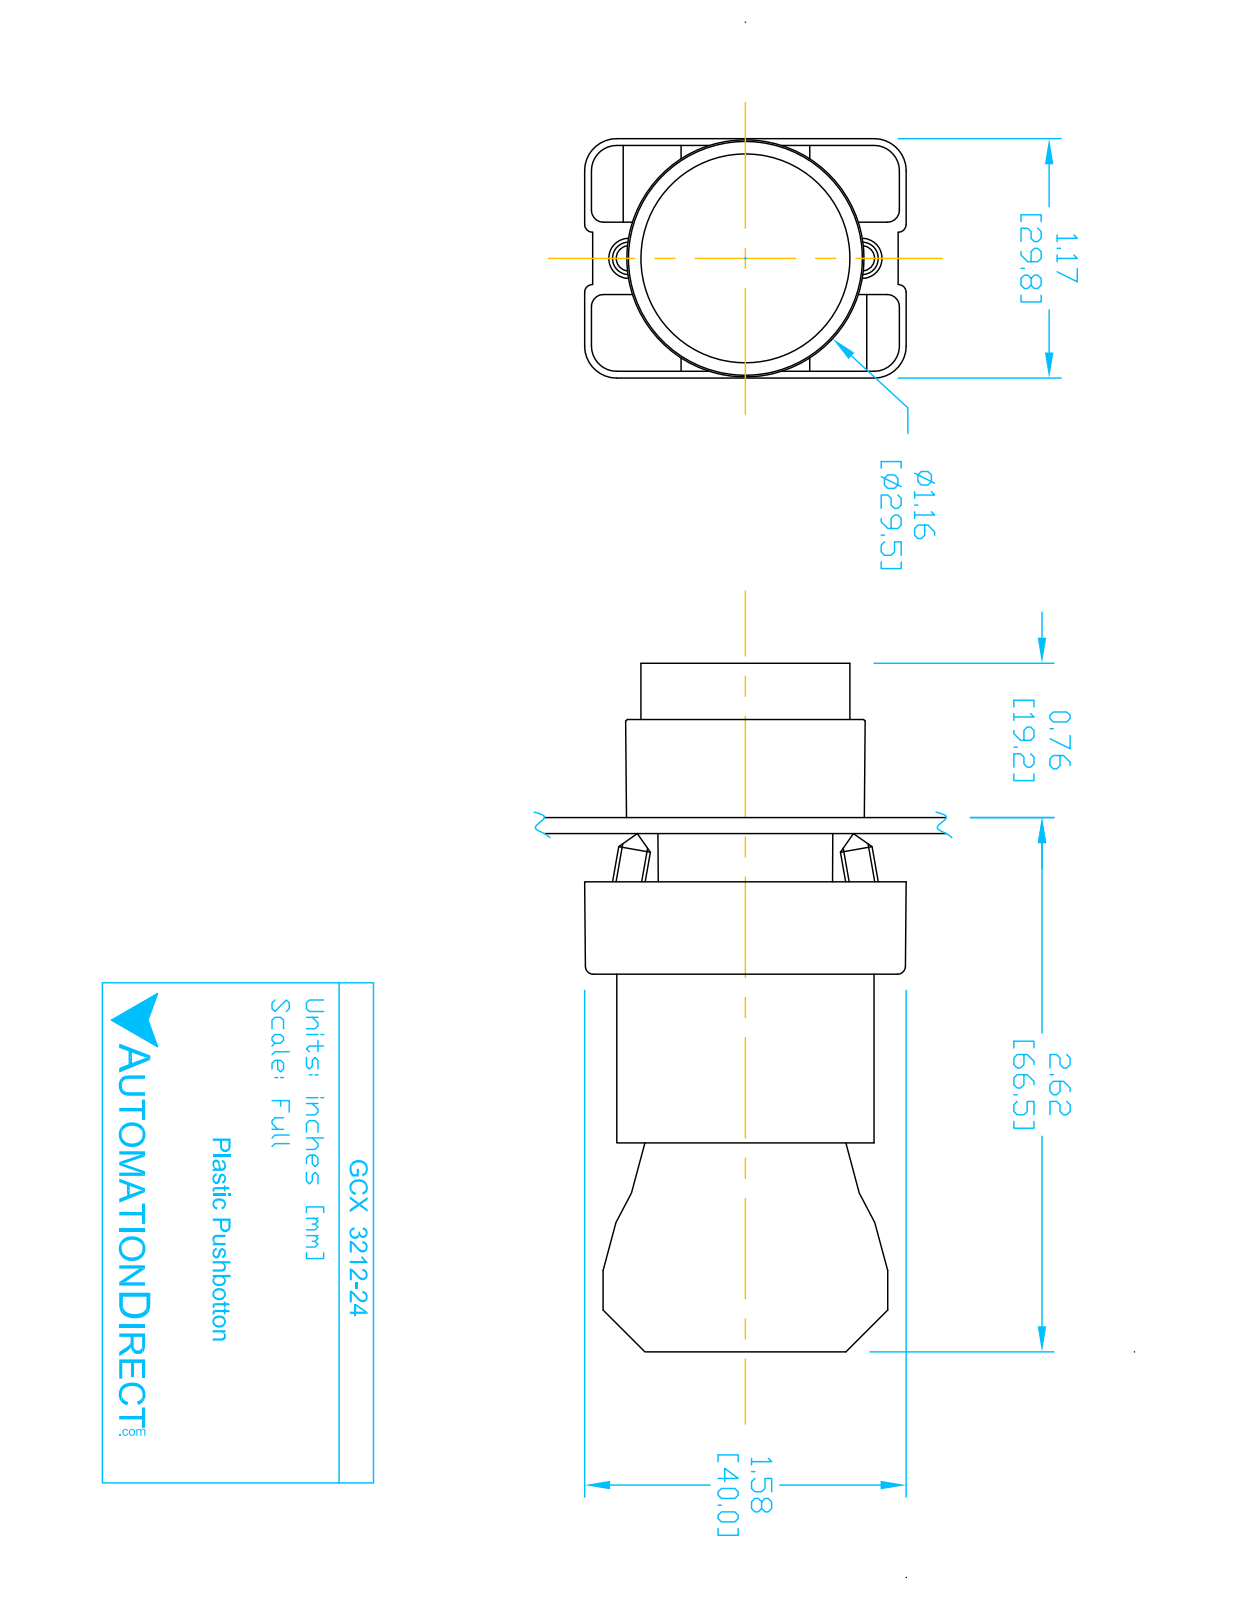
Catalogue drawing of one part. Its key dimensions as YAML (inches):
part_name: "ecx1040; GCX3212 OPERATOR; ECX3029-2; GCX3212-24 (+1 more)"
step_written_by: "SolidWorks 2016 (AUTOMOTIVE_DESIGN)"
units: inches
bodies: {solids: 7, faces: 425, planar: 250, cylindrical: 144, other: 31}
overall_size: [3.319, 1.581, 1.177]
volume: 2.721
surface_area: 36.32
round_holes:
  - {diameter: 0.079, count: 2}
  - {diameter: 0.124, count: 2}
  - {diameter: 0.13, count: 2}
  - {diameter: 0.087, count: 1}
  - {diameter: 0.197, count: 1}
  - {diameter: 0.469, count: 1}
  - {diameter: 0.878, count: 1}
  - {diameter: 0.888, count: 1}
  - {diameter: 1.024, count: 1}
round_bosses_or_shafts:
  - {diameter: 0.157, count: 4}
  - {diameter: 1.175, count: 1}
  - {diameter: 1.004, count: 1}
  - {diameter: 0.945, count: 1}
  - {diameter: 0.856, count: 1}
  - {diameter: 0.78, count: 1}
  - {diameter: 0.504, count: 1}
partial_cylinders:
  - {radius: 0.059, count: 24}
  - {radius: 0.041, count: 12}
  - {radius: 0.124, count: 12}
  - {radius: 0.157, count: 12}
  - {radius: 0.039, count: 8}
  - {radius: 0.128, count: 2}
  - {radius: 0.02, count: 1}
  - {radius: 0.063, count: 1}
face_to_face_distances: [0.827, 0.579, 1.171, 2.02, 1.193, 0.031, 0.033, 0.573, 1.165, 0.593]
hole_center_spacings: [0.236, 0.544, 0.472, 0.49]
